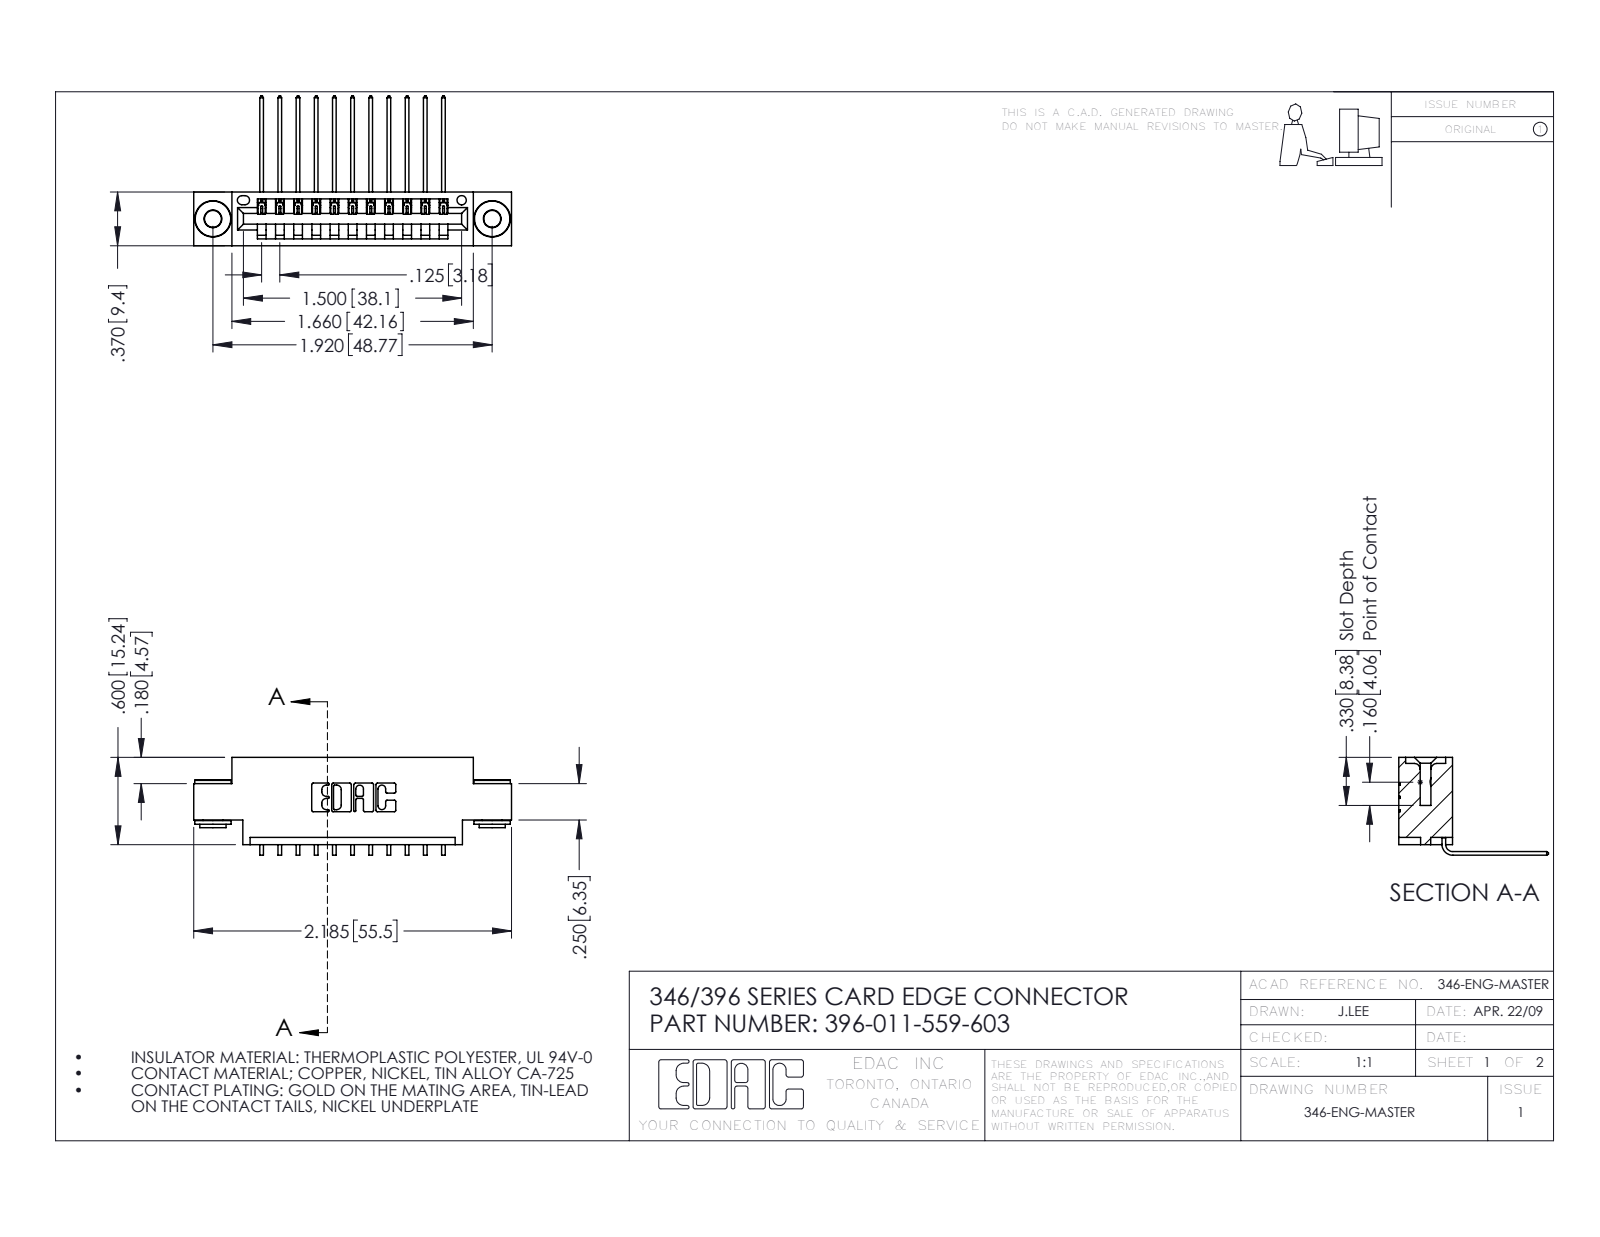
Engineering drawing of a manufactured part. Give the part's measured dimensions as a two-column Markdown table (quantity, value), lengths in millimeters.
| quantity | value |
| --- | --- |
| part name | 346 Part_0.170 Offset - 0.156 Dia-TH; 396-011-559-603; 345-250-002_345-250-002-102; 345-292-001_558 559 Tail - 1 |
| STEP written by | SolidWorks 2016 (CONFIG_CONTROL_DESIGN) |
| units | millimeters |
| bodies | 14 solids, 824 faces (552 planar, 264 cylindrical, 8 other) |
| overall size | 55.5 × 26.2 × 17.1 |
| volume | 5 000 mm³ |
| surface area | 6 516 mm² |
| round holes (diameter × count) | 2.9 × 2, 4 × 2, 1.6 × 1 |
| round bosses / shafts (diameter × count) | 6.4 × 2, 4.6 × 2, 3.5 × 2 |
| partial cylindrical surfaces (radius × count) | 0.2 × 22, 0.3 × 22, 0.2 × 6, 0.8 × 6, 0.7 × 3, 0.8 × 2, 1 × 2, 0.4 × 1 |
| main face-to-face distances | 6.4, 9.4, 1.2, 8.2, 0.6, 1.8, 3.8, 5.6, 2.5, 4.4 |
| hole center spacings | 6.2, 43.6, 48.8 |
